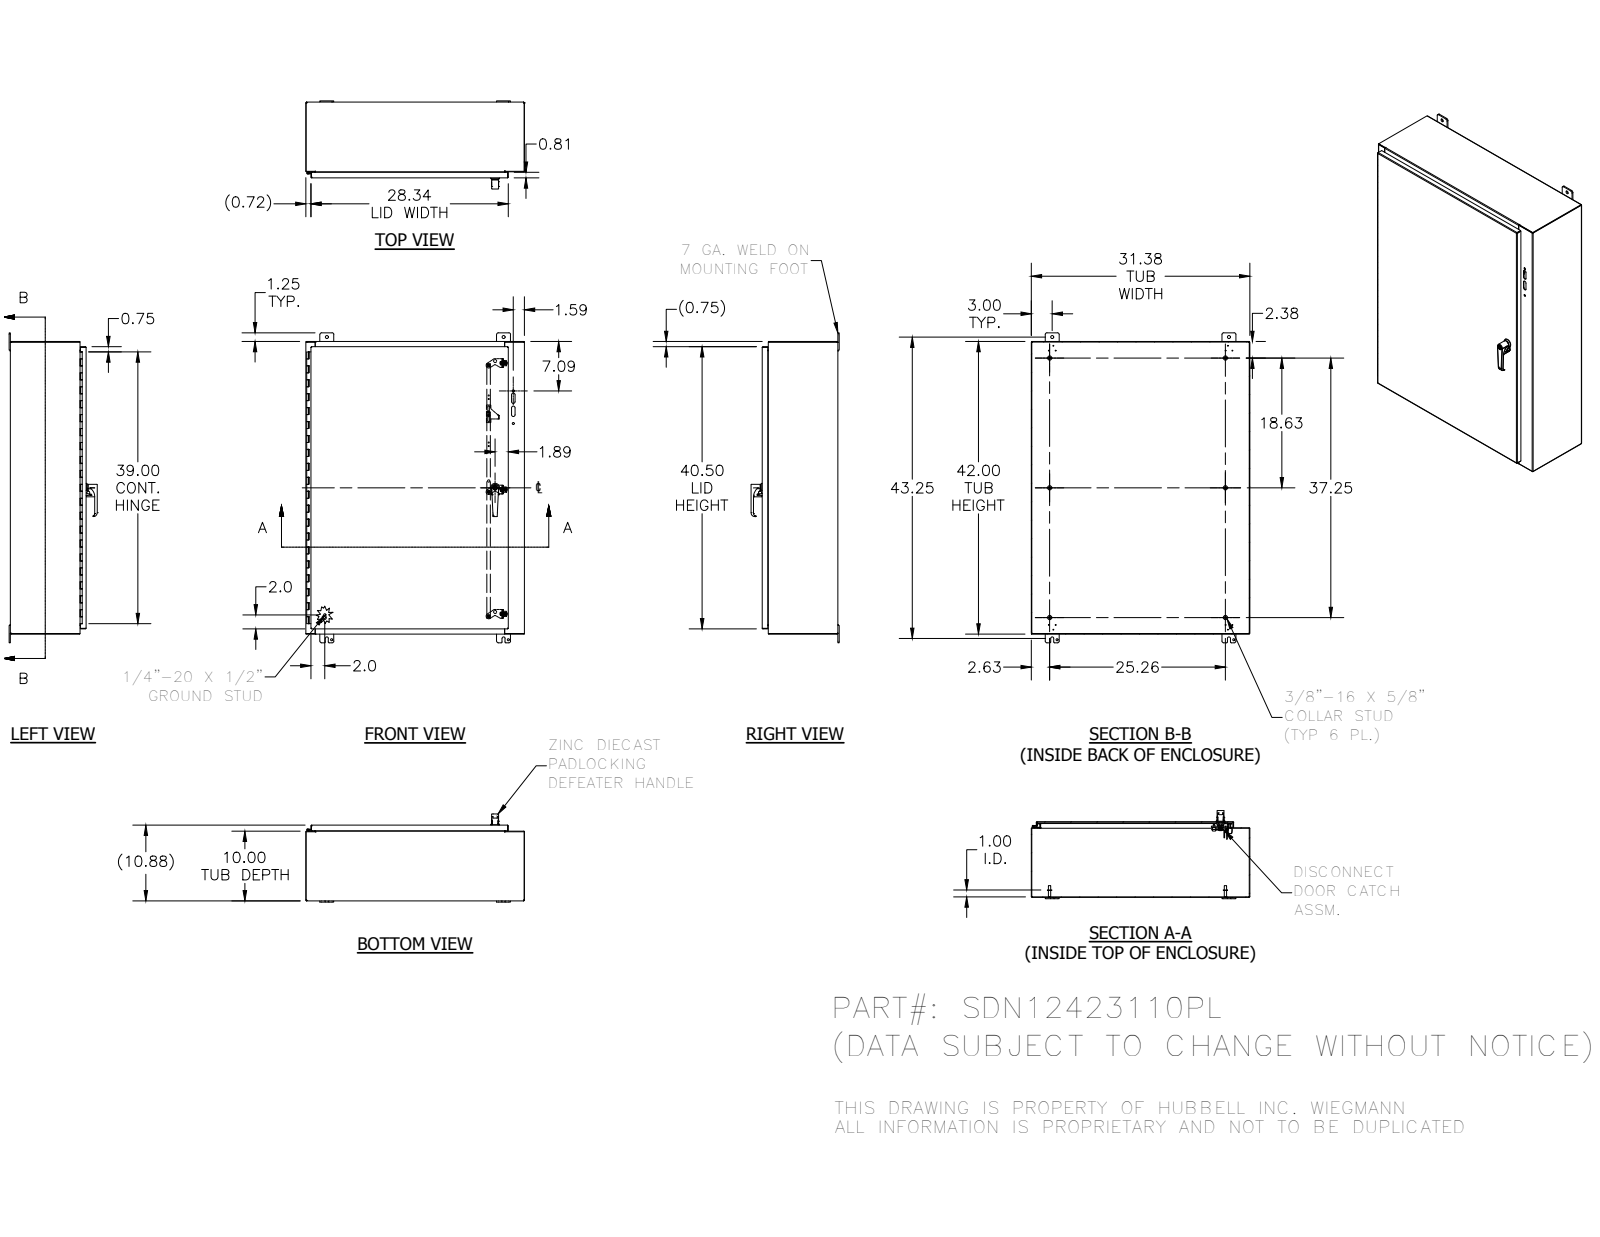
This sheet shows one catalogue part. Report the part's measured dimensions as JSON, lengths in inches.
{"part_name": "SDN12423110PL; SDN12423110PLBKP; 388116; 34840 (+8 more)", "step_written_by": "Autodesk Inventor 2012 (AUTOMOTIVE_DESIGN)", "units": "inches", "bodies": {"solids": 60, "faces": 1883, "planar": 978, "cylindrical": 643, "other": 262}, "overall_size": [44.5, 31.38, 12.649], "volume_in3": 341.3, "surface_area_in2": 9133, "round_holes": [[0.12, 12], [0.145, 6], [0.313, 4], [0.32, 4], [0.438, 4], [0.196, 3], [0.211, 3], [0.22, 3], [0.313, 3], [0.45, 3], [0.156, 2], [0.281, 2]], "round_bosses_or_shafts": [[0.625, 8], [0.33, 8], [0.437, 6], [0.3, 6], [0.225, 6], [0.25, 4], [0.19, 4], [0.75, 3]], "partial_cylinders_radius": [[0.02, 38], [0.012, 30], [0.025, 24], [0.25, 23], [0.125, 21], [0.031, 20], [0.105, 20], [0.07, 8]], "face_to_face_distances": [0.074, 10.801, 10.727, 10.875, 31.306, 41.926, 9.926, 0.875, 31.232, 31.38], "hole_center_spacings": [17.844, 18.156, 0.759, 24.746, 25.38, 36, 39.38, 39.392]}
